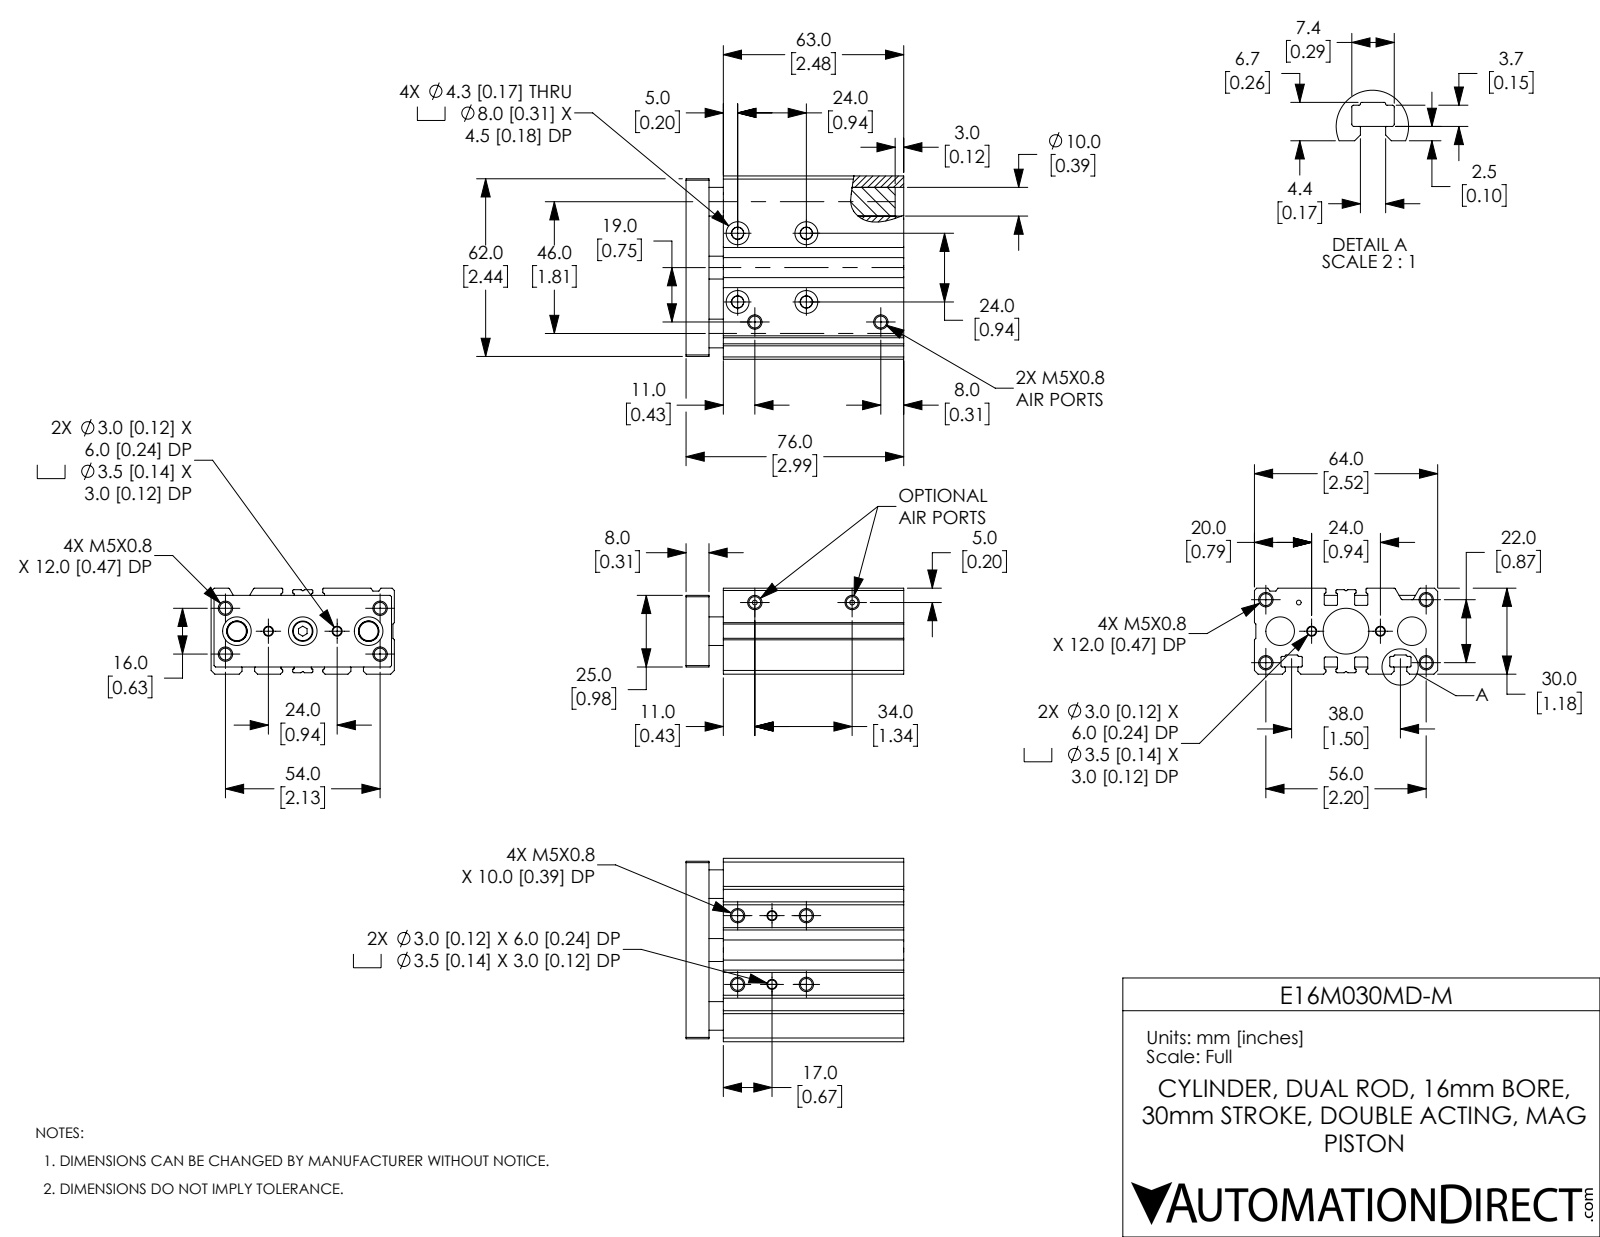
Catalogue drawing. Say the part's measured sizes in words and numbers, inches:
The part is named "E16M030MD-M_BODY; E16M030MD-M; E16M030MD-M_ENDPLATE". Its 3-D file was written by "SolidWorks 2019 (CONFIG_CONTROL_DESIGN)". It is 5 solids with 411 faces: 133 planar, 192 cylindrical and 86 other. Overall it measures 2.992 by 2.52 by 1.181 inches. Its volume is 6.725 cubic inches and its surface area 67.69 square inches. Round holes: 16 of diameter 0.163, 4 of diameter 0.118, 4 of diameter 0.138, 4 of diameter 0.169, 4 of diameter 0.315, 3 of diameter 0.066, 3 of diameter 0.197, 3 of diameter 0.394, 2 of diameter 0.28, 1 of diameter 0.394, 1 of diameter 0.63, 1 of diameter 0.63. Round bosses or shafts: 1 of diameter 0.315, 1 of diameter 0.28. Partial cylindrical surfaces (rounded edges, fillets, slot ends): 22 of radius 0.008, 20 of radius 0.016, 8 of radius 0.01, 6 of radius 0.012, 4 of radius 0.02. The main face-to-face distances are 1.181, 0.02, 2.52, 2.48, 1.083, 0.138, 0.236, 2.677, 0.197, 1.142. The hole center spacings are 0.472, 0.945, 0.124, 0.352, 0.476, 0.669, 0.749, 0.765.
